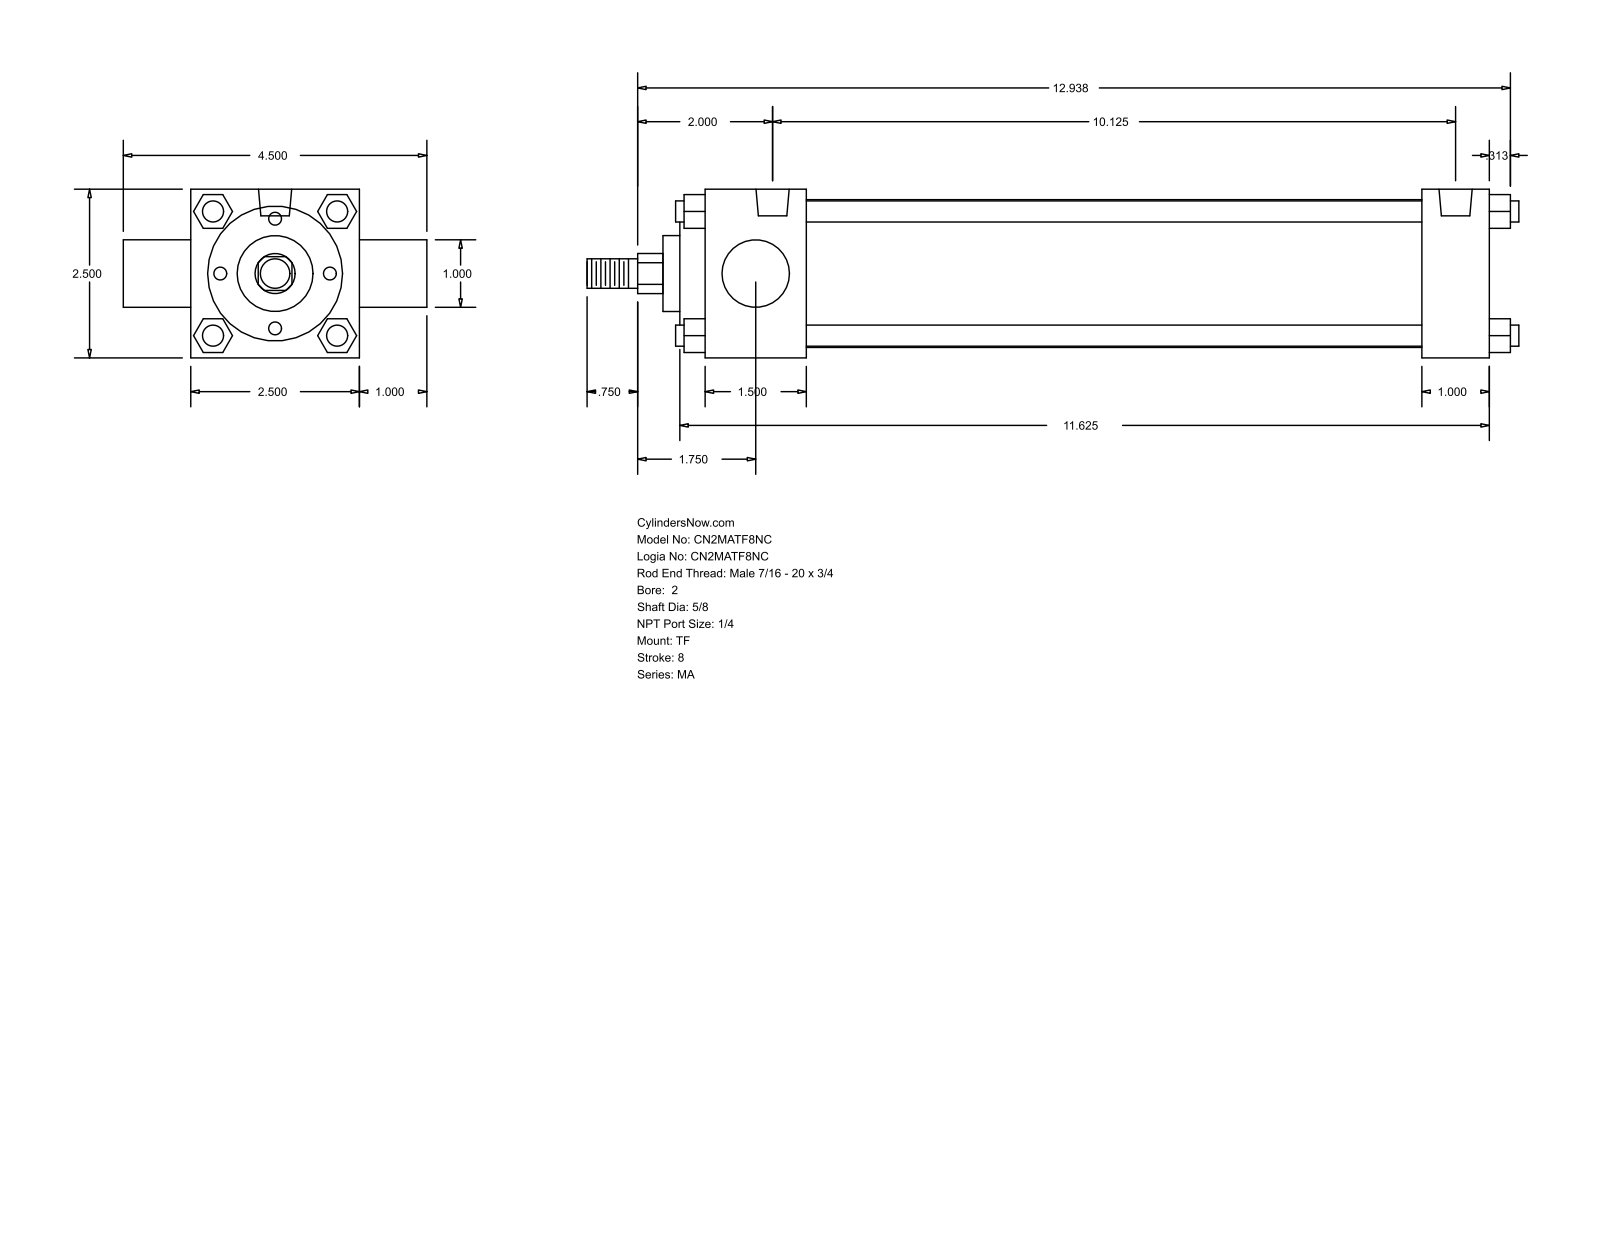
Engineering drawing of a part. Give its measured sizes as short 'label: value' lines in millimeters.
name: MA_TF__0200_0.625
written by: GSSL Pune (CONFIG_CONTROL_DESIGN)
unit: mm
bodies: 0 solids, 122 faces (93 planar, 29 cylindrical, 0 other)
size: 350.84 × 114.3 × 63.5
holes: 3× ⌀7.94, 2× ⌀12.49
bosses: 4× ⌀7.94, 1× ⌀55.63, 1× ⌀50.8, 1× ⌀28.57, 1× ⌀25.4, 1× ⌀15.88, 1× ⌀11.11
rounds: 1× R7.54
face distances: 63.5, 38.1, 12.7, 295.28, 269.87, 231.77, 257.18, 25.41, 9.52, 47.62
hole spacings: 257.18
